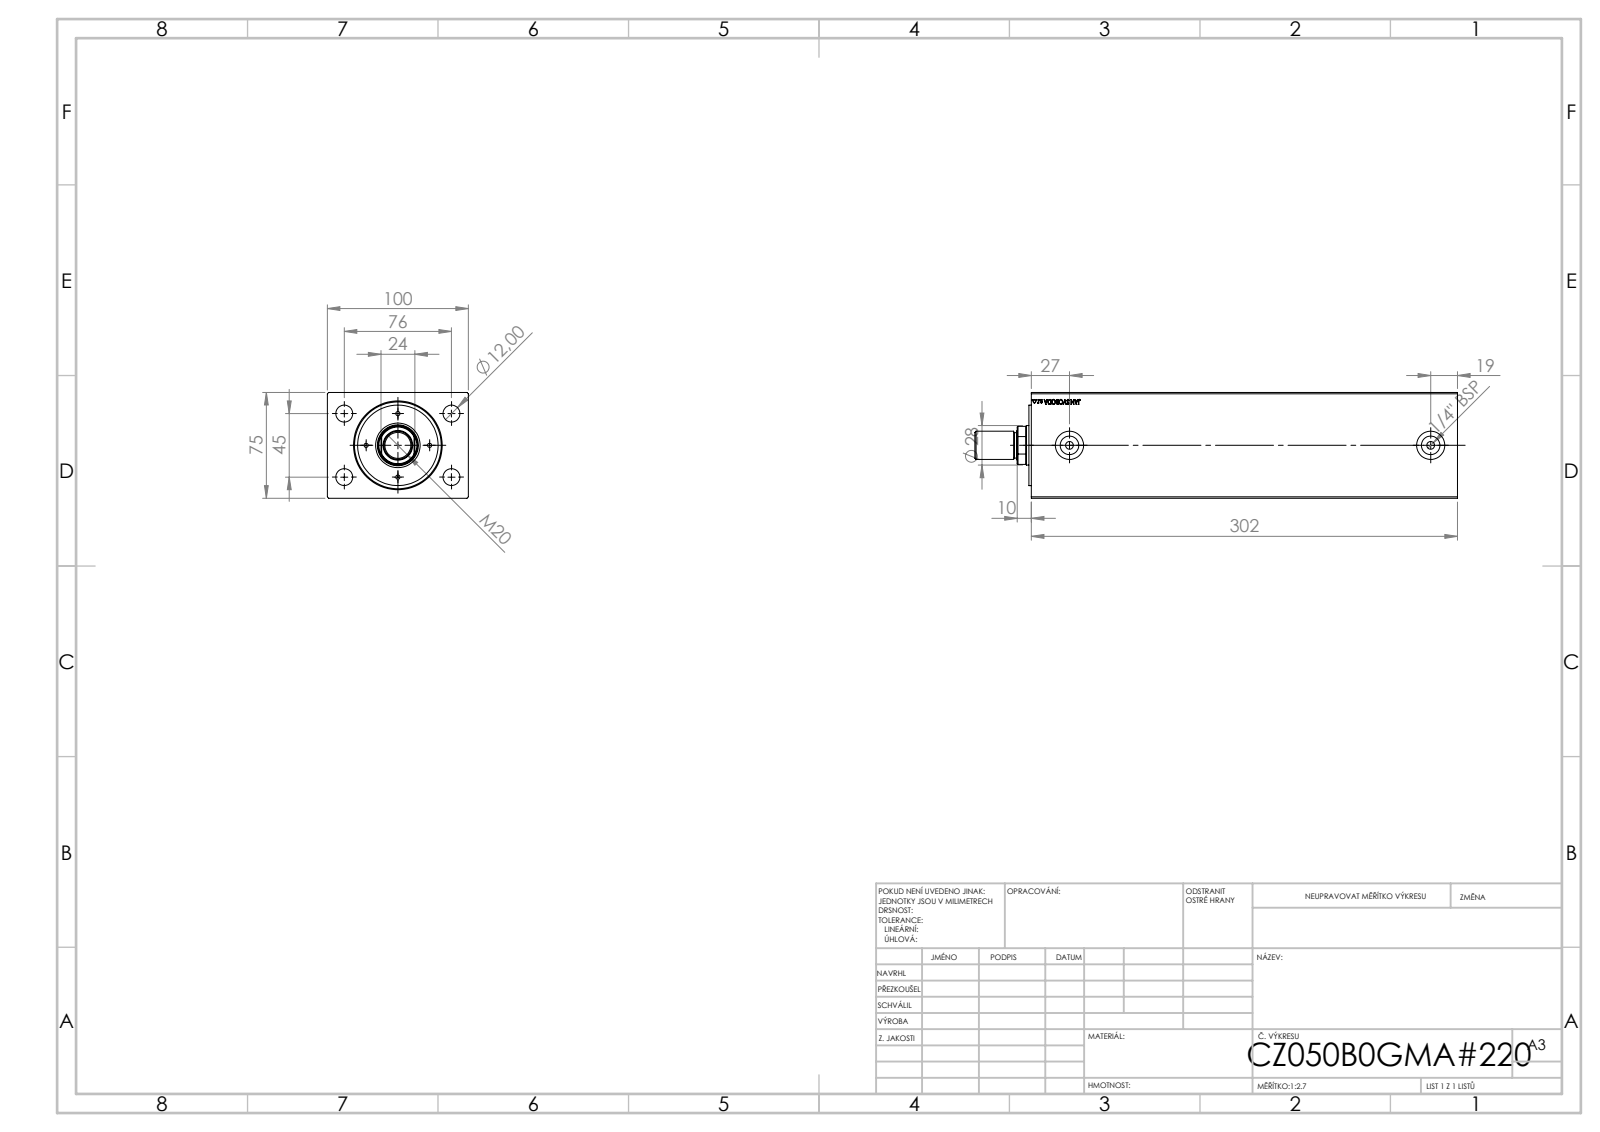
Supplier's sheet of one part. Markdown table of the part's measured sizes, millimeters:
| quantity | value |
| --- | --- |
| part name | V500CZ; V500CZ_B_VC; V500CZ_MALE_METRIC |
| STEP written by | SolidWorks 2019 (CONFIG_CONTROL_DESIGN) |
| units | millimeters |
| bodies | 4 solids, 887 faces (403 planar, 62 cylindrical, 422 other) |
| overall size | 342 × 100 × 75 |
| volume | 2 020 000 mm³ |
| surface area | 241 133 mm² |
| round holes (diameter × count) | 3 × 4, 12 × 4, 5.5 × 2, 13.16 × 2, 20 × 2, 18.5 × 1, 28 × 1, 29 × 1, 36 × 1, 50 × 1, 61.5 × 1 |
| round bosses / shafts (diameter × count) | 57 × 1, 20 × 1, 18 × 1 |
| partial cylindrical surfaces (radius × count) | 13.5 × 1 |
| main face-to-face distances | 75, 100, 302, 284.5, 17.5, 82, 202.5, 220, 1.8, 83.8 |
| hole center spacings | 22.5, 27.32, 31.82, 38, 44.16, 45, 58.9, 64.55 |
